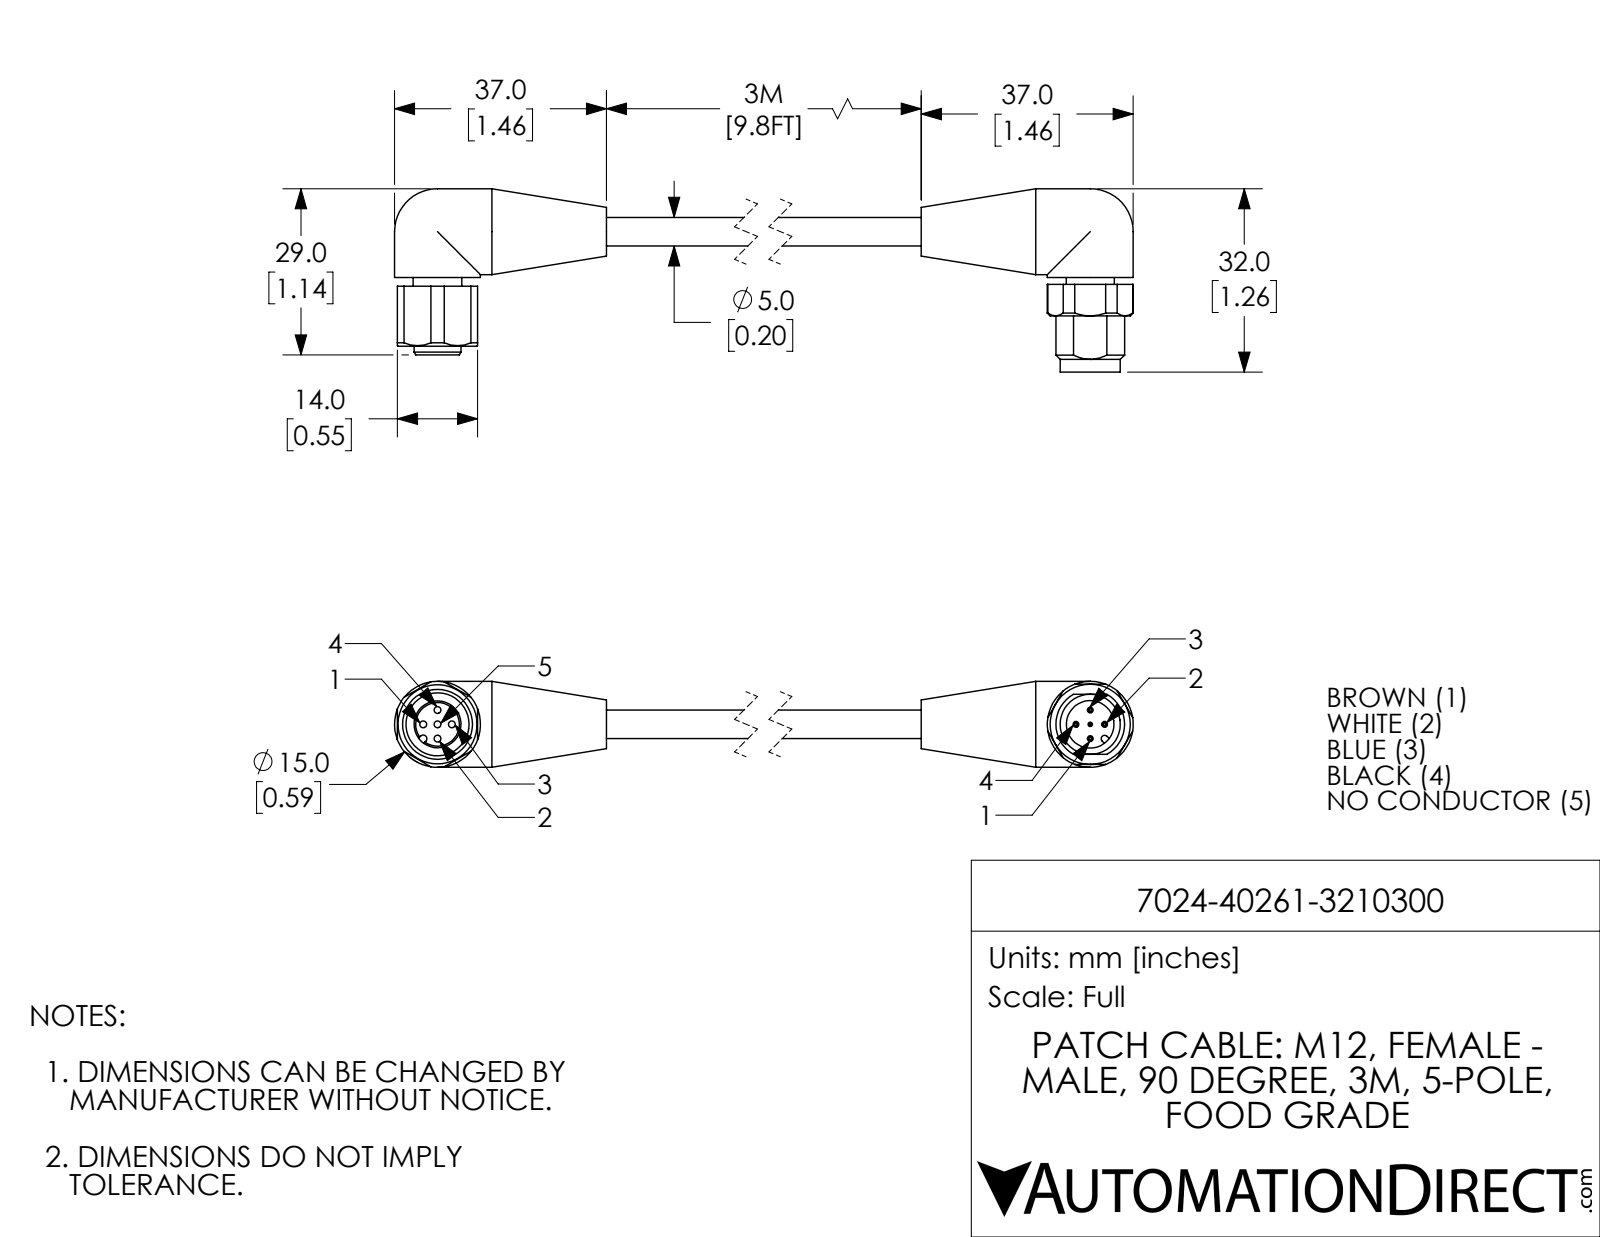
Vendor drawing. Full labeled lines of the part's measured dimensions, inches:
Part name (STEP PRODUCT): 7024-40261-3210300_MALE; 7024-40261-3210300; 7024-40261-3210300_FEMALE
STEP written by: SolidWorks 2018 (AUTOMOTIVE_DESIGN)
Units: inches
Bodies: 2 solids, 135 faces (43 planar, 61 cylindrical, 31 other)
Overall size (bounding box): 5.776 × 1.26 × 0.591
Volume: 0.892 in³ · Surface area: 10.83 in²
Round holes (diameter × count): ⌀0.047 ×5, ⌀0.327 ×1, ⌀0.433 ×1
Round bosses / shafts (diameter × count): ⌀0.039 ×4, ⌀0.591 ×3, ⌀0.413 ×1, ⌀0.335 ×1, ⌀0.331 ×1, ⌀0.323 ×1, ⌀0.197 ×1
Partial cylindrical surfaces — rounded edges, fillets, slot ends (radius × count): R0.024 ×1, R0.026 ×1, R0.236 ×1
Main face-to-face distances: 0.551, 0.059, 0.047, 0.472, 0.413, 0.177, 0.118, 0.069, 0.482, 0.217
Hole centre spacings: 0.098, 0.139, 0.197, 5.186, 5.087, 5.185, 5.283
